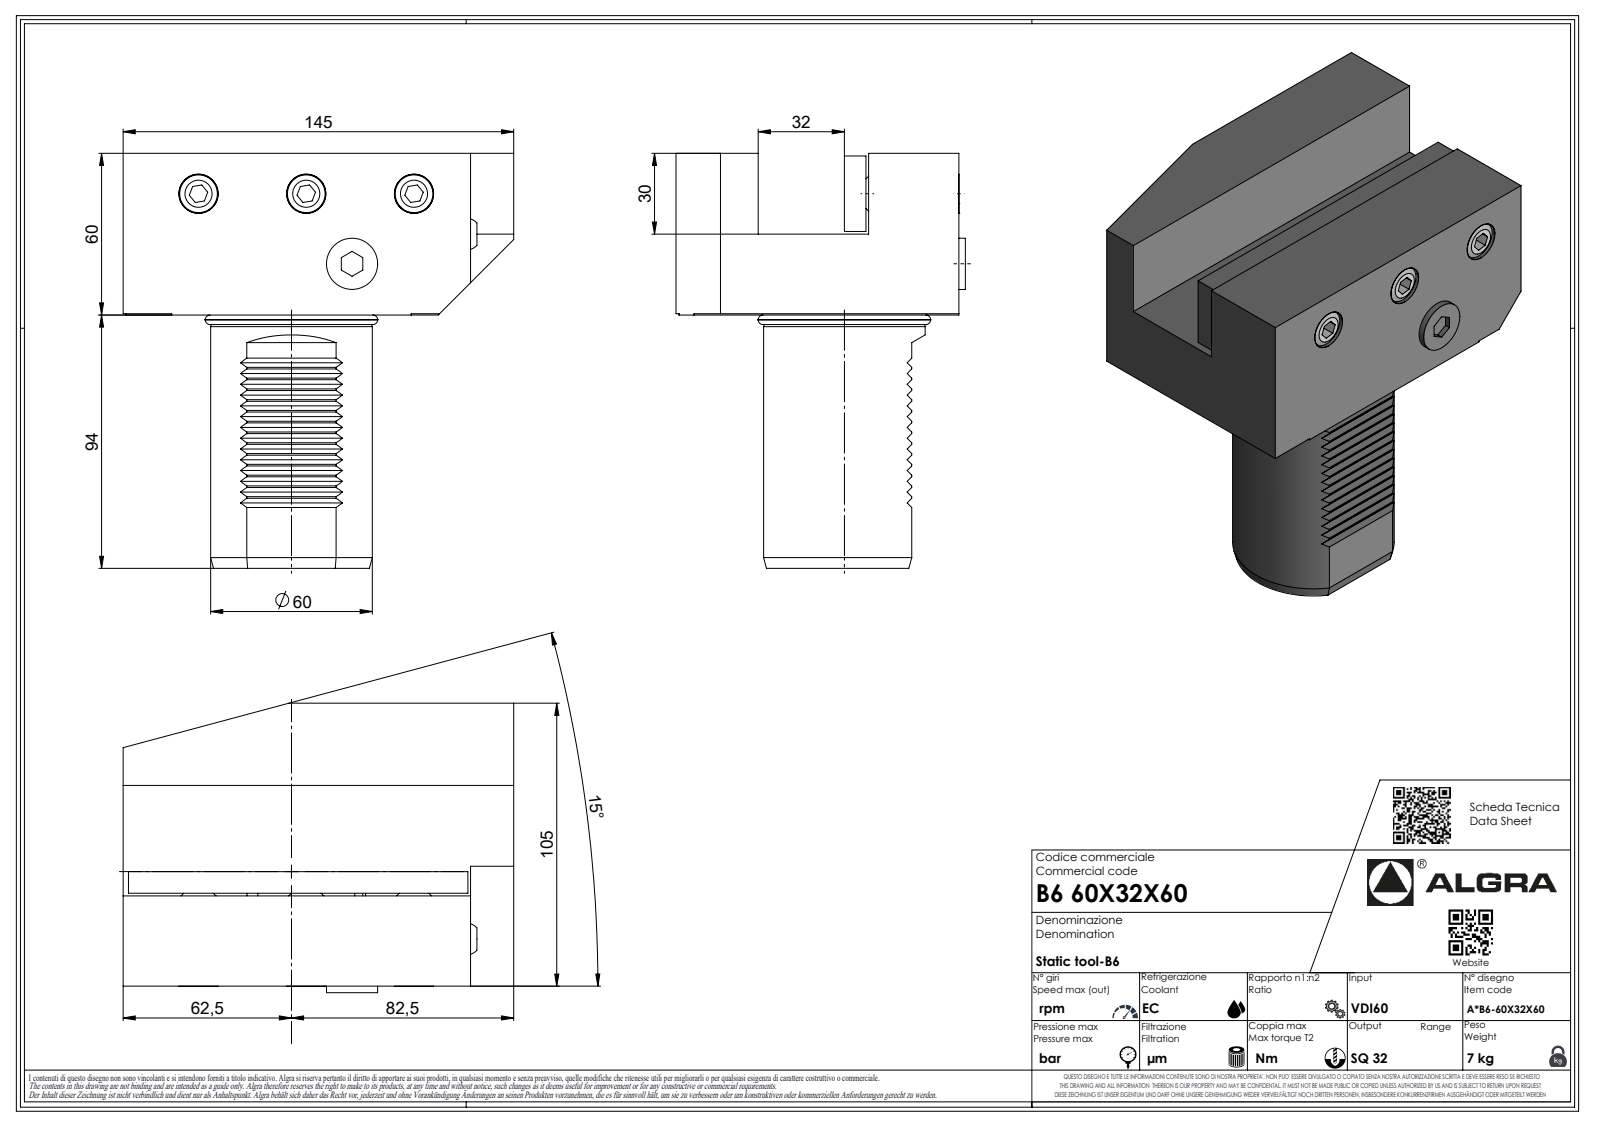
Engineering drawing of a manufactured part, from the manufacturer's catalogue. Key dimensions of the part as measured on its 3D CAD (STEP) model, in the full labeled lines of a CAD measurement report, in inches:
Part name (STEP PRODUCT): B660X32X60
STEP written by: SolidWorks 2023 (AUTOMOTIVE_DESIGN)
Units: inches
Bodies: 1 solid, 349 faces (228 planar, 32 cylindrical, 89 other)
Overall size (bounding box): 6.063 × 5.709 × 4.228
Volume: 56.6 in³ · Surface area: 127.3 in²
Round holes (diameter × count): ⌀0.083 ×1
Round bosses / shafts (diameter × count): ⌀2.527 ×1, ⌀2.362 ×1, ⌀0.748 ×1, ⌀0.251 ×1, ⌀0.067 ×1
Partial cylindrical surfaces — rounded edges, fillets, slot ends (radius × count): R0.013 ×7, R0.02 ×7, R0.146 ×7, R0.008 ×1, R2.421 ×1
Main face-to-face distances: 1.181, 2.362, 1.201, 4.134, 2.933, 2.461, 1.26, 1.673, 0.039, 6.063
